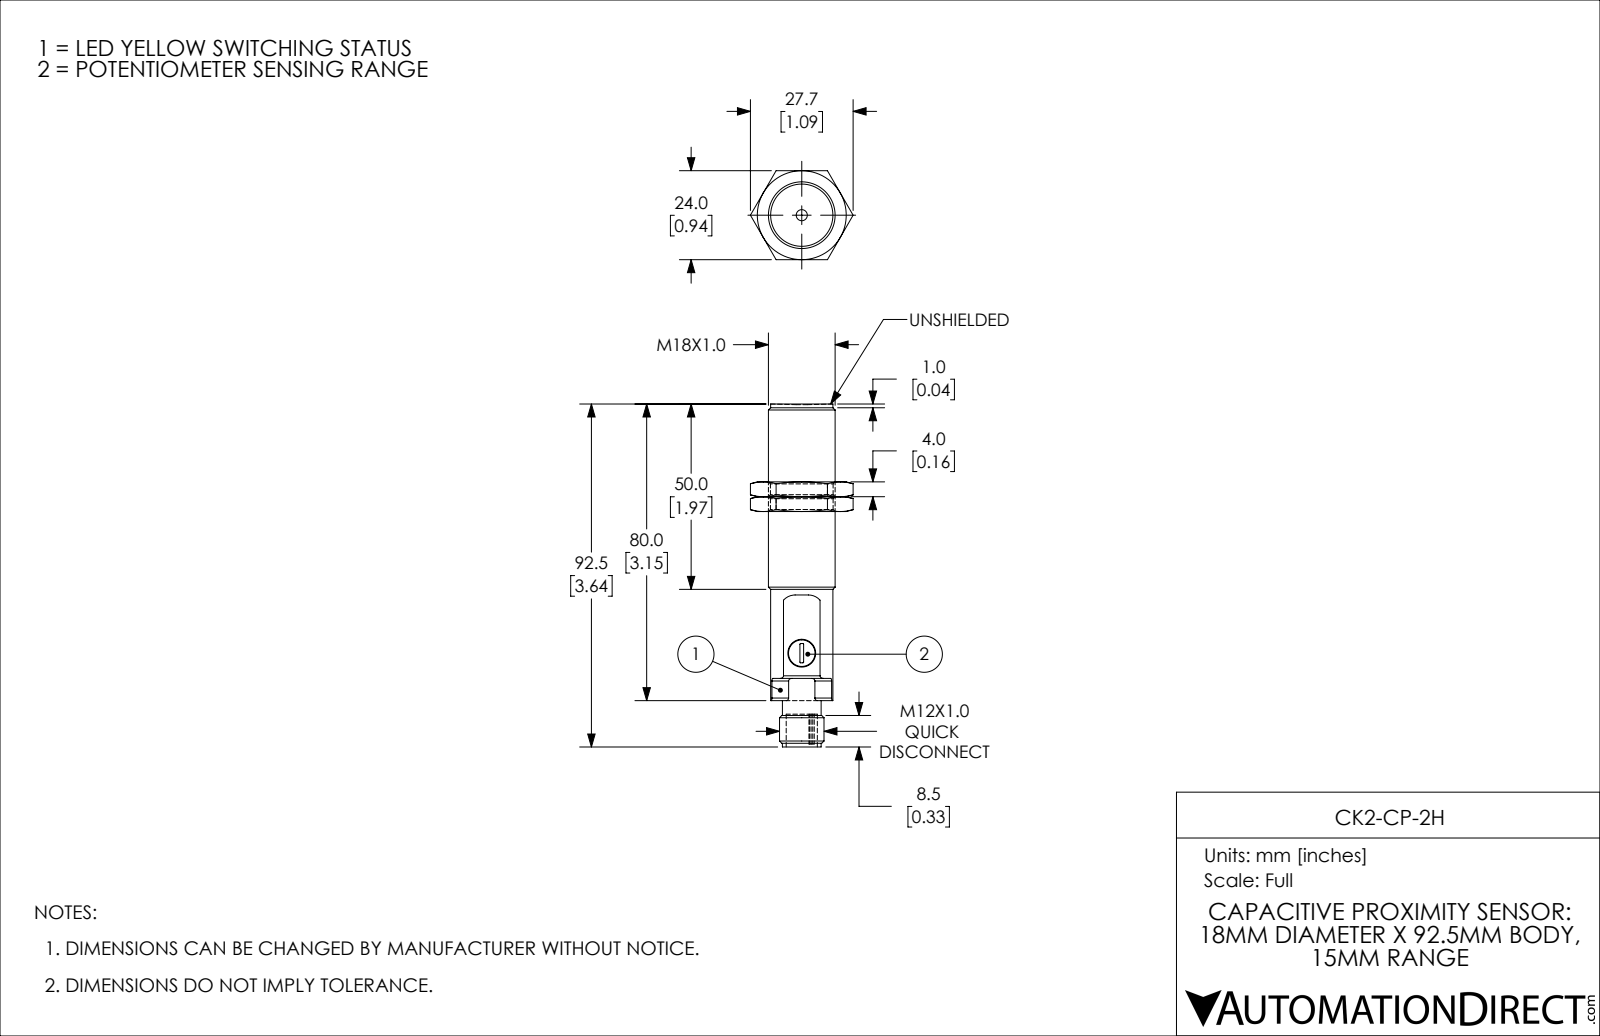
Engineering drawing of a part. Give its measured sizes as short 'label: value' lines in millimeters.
name: CK2-CP-2H
written by: SolidWorks 2018 (AUTOMOTIVE_DESIGN)
unit: mm
bodies: 3 solids, 92 faces (35 planar, 22 cylindrical, 35 other)
size: 92.5 × 27.7 × 24
volume: 21 610 mm³; area: 7 632 mm²
holes: 1× ⌀8.4, 1× ⌀16.9
bosses: 1× ⌀18, 1× ⌀16.8, 1× ⌀12, 1× ⌀10.4, 1× ⌀7.5
rounds: 4× R0.2, 3× R0.7, 2× R4.2, 1× R0.6
face distances: 4, 24, 8, 5.2, 18.8, 55, 59, 51, 3.7, 54.7
hole spacings: 1.4
